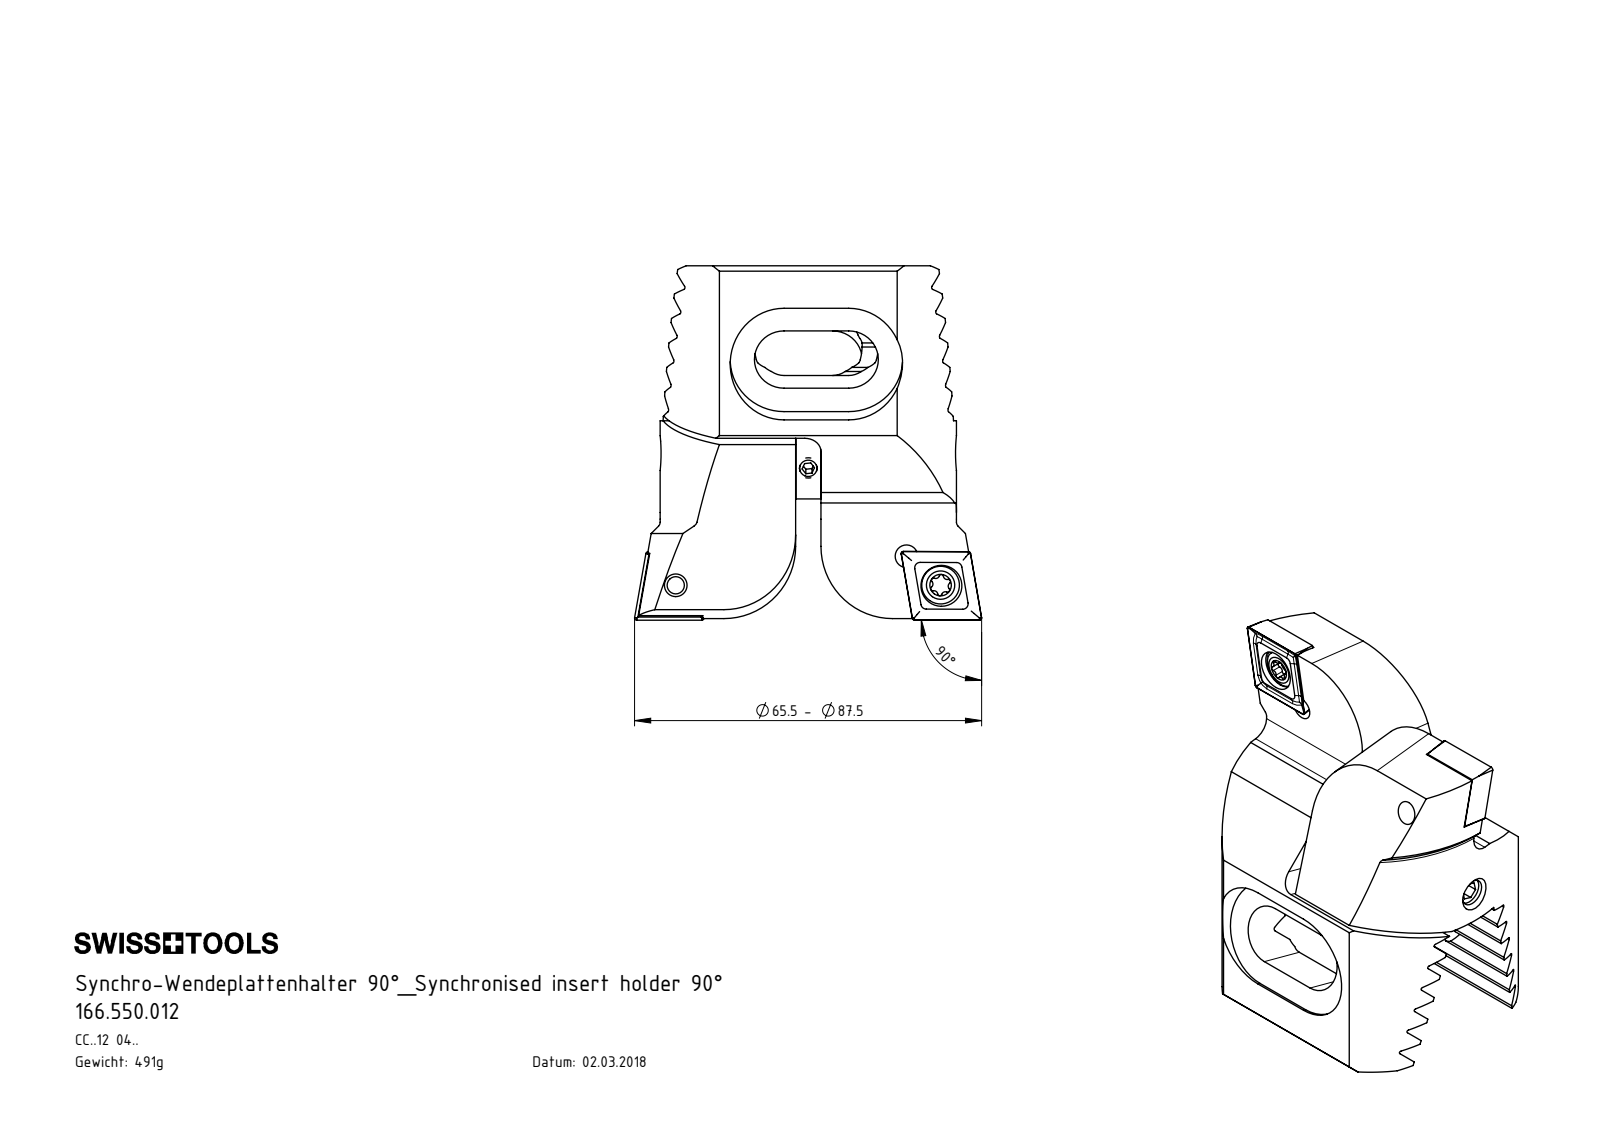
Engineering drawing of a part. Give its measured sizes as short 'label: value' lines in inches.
name: Z55-WCC.001.037_A; 166.550.012; Z55-ER3.001.052_A; CCMT120404 (+4 more)
written by: SolidWorks 2017 (CONFIG_CONTROL_DESIGN)
unit: in
bodies: 11 solids, 484 faces (187 planar, 155 cylindrical, 142 other)
size: 2.589 × 2.536 × 1.732
volume: 3.818 in³; area: 37.39 in²
holes: 4× ⌀0.165, 3× ⌀0.039, 3× ⌀0.13, 2× ⌀0.217, 2× ⌀0.299, 1× ⌀0.197
bosses: 3× ⌀0.157, 2× ⌀0.276, 2× ⌀0.197, 1× ⌀0.669, 1× ⌀0.236, 1× ⌀0.15
rounds: 12× R0.013, 12× R0.015, 12× R0.027, 8× R0.039, 4× R0.118, 4× R0.217, 4× R0.394, 2× R0.524
face distances: 0.16, 0.32, 0.481, 0.641, 0.801, 0.191, 0.679, 0.039, 0.28, 0.854
hole spacings: 0.326, 0.118, 0.334, 0.335, 0.59, 0.591, 0.602, 1.117
